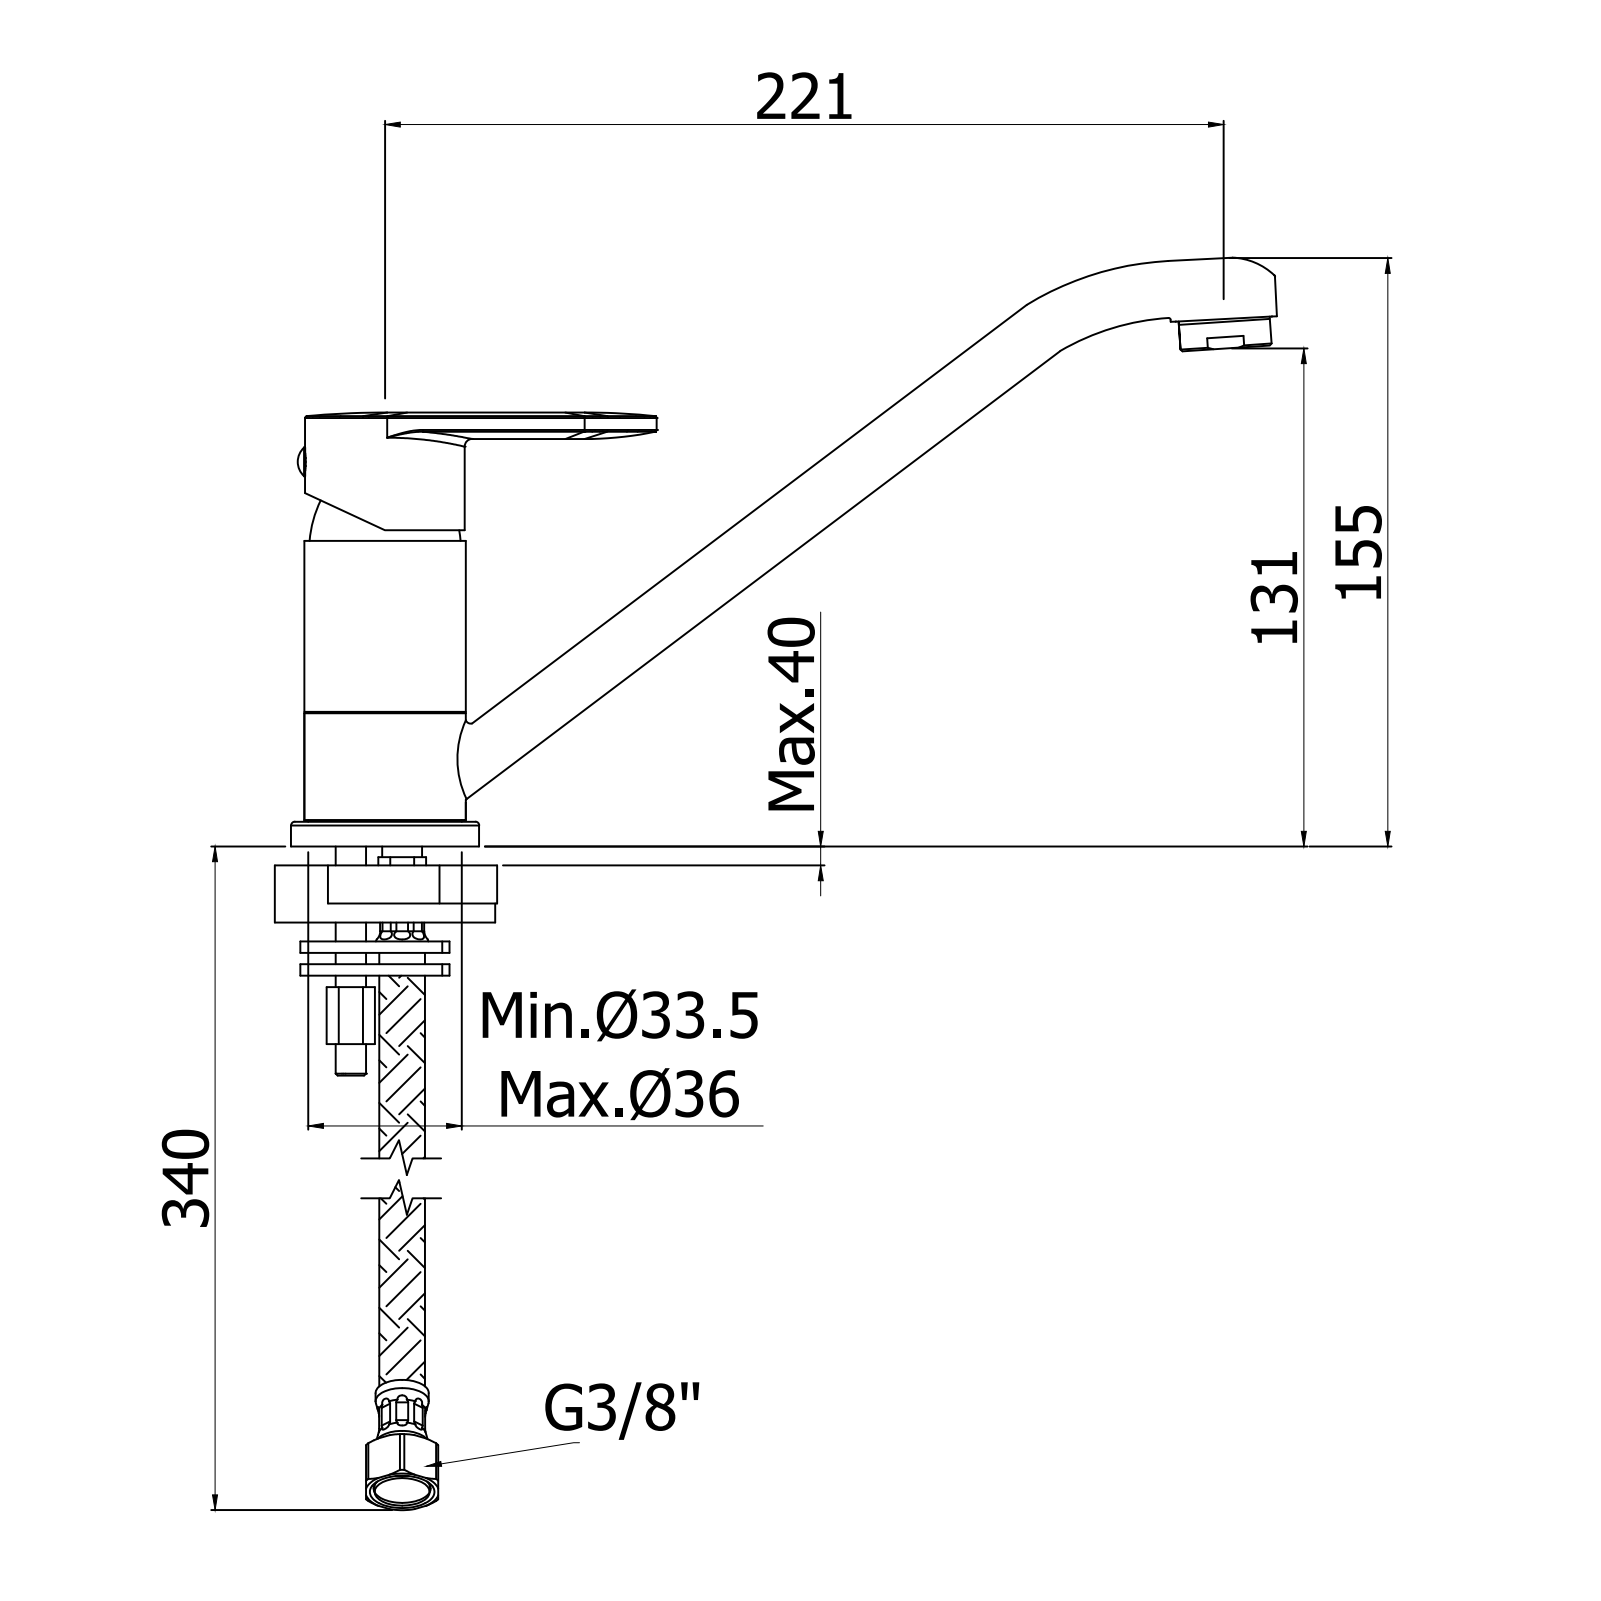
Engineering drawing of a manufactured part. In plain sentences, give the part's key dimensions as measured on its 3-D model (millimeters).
The part is named "CA182TCR". Its 3-D file was written by "CREO PARAMETRIC BY PTC INC, 2020044 (CONFIG_CONTROL_DESIGN)". It is 0 solids with 89 faces: 14 planar, 19 cylindrical and 56 other. Overall it measures 258.72 by 159.1 by 49.5 millimeters. Round bosses or shafts: 1 of diameter 49.5, 1 of diameter 43, 1 of diameter 42.5, 1 of diameter 28, 1 of diameter 24, 1 of diameter 7.6. Partial cylindrical surfaces (rounded edges, fillets, slot ends): 2 of radius 4, 1 of radius 14.64, 1 of radius 20, 1 of radius 137. The main face-to-face distances are 6.5, 80.4, 73.9, 7.7, 82, 75.5, 1.6, 22, 4.7, 3.
